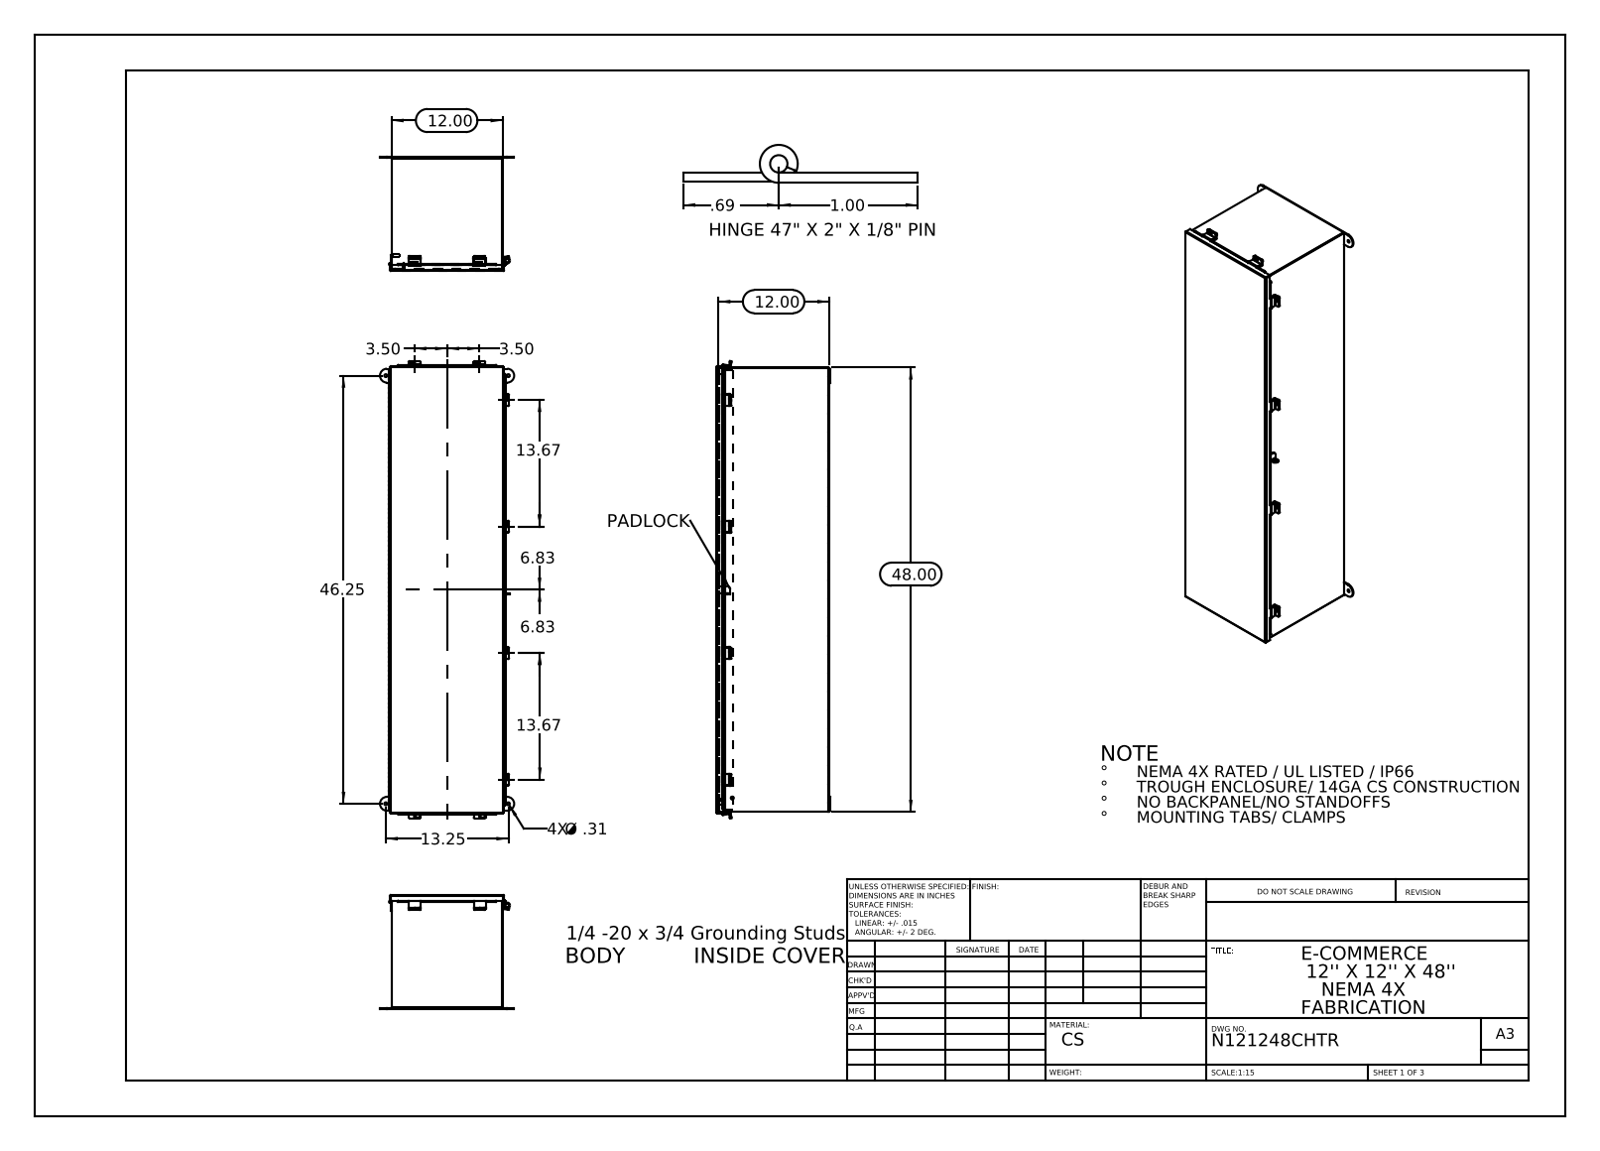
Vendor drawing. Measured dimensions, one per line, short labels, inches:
name: N121248SSCHTR JIC Cover Clamp; N121248SSCHTR JIC Mounting Bracket; N121248SSCHTR; N121248SSCHTR JIC Top (+8 more)
written by: SolidWorks 2013 (CONFIG_CONTROL_DESIGN)
unit: in
bodies: 27 solids, 1468 faces (889 planar, 559 cylindrical, 20 other)
size: 49.407 × 14.5 × 12.337
volume: 216.7 in³; area: 5 809 in²
holes: 8× ⌀0.25, 4× ⌀0.313, 1× ⌀0.125, 1× ⌀0.125, 1× ⌀0.375
bosses: 2× ⌀0.315, 2× ⌀0.236, 1× ⌀0.273, 1× ⌀0.25
rounds: 30× R0.125, 16× R0.133, 12× R0.009, 10× R0.013, 10× R0.088, 6× R0.083, 6× R0.1, 4× R0.75
face distances: 0.075, 11.925, 12.128, 12, 11.85, 12.203, 12.053, 47.925, 47.85, 48
hole spacings: 7, 13.25, 13.666, 27.332, 46.25, 48.111, 12.632, 13.666
